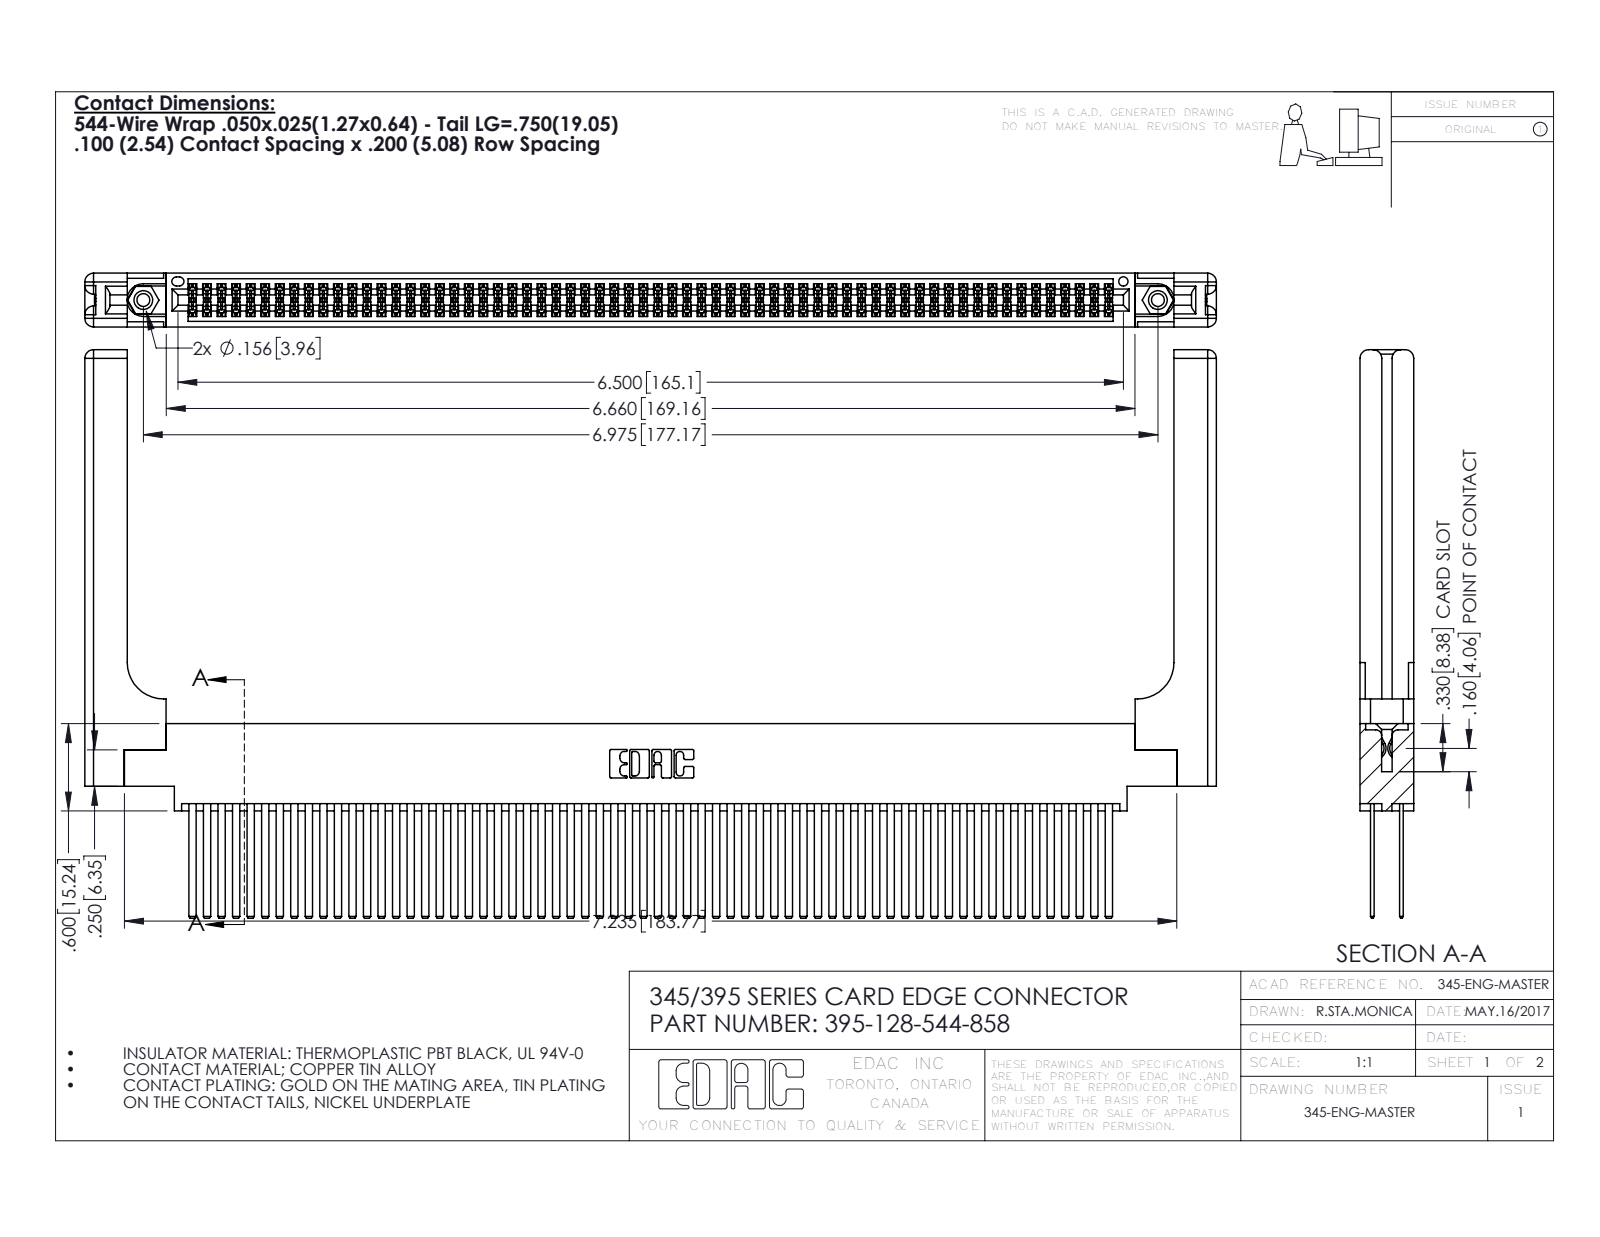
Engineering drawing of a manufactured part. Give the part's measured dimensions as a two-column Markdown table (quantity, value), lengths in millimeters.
| quantity | value |
| --- | --- |
| part name | 345-250-001_345-250-001-102; 345 Part_0.170 Offset - 0.156 Dia-TH; 395-128-544-858; 345-220-058_345-220-058 (+1 more) |
| STEP written by | SolidWorks 2016 (CONFIG_CONTROL_DESIGN) |
| units | millimeters |
| bodies | 133 solids, 6018 faces (3944 planar, 2014 cylindrical, 60 other) |
| overall size | 197.6 × 99.2 × 9.4 |
| volume | 29 550 mm³ |
| surface area | 42 050 mm² |
| round holes (diameter × count) | 2.3 × 2, 3.2 × 2, 4 × 2, 1.6 × 1 |
| round bosses / shafts (diameter × count) | 3.9 × 2 |
| partial cylindrical surfaces (radius × count) | 0.2 × 192, 0.3 × 22, 1.5 × 16, 0.2 × 6, 0.8 × 6, 0.7 × 3, 0.4 × 2, 0.5 × 2 |
| main face-to-face distances | 1.8, 7.6, 2.5, 6.9, 0.6, 5.1, 9.4, 5.7, 4.4, 3.8 |
| hole center spacings | 6.9, 171.2, 177.2 |
